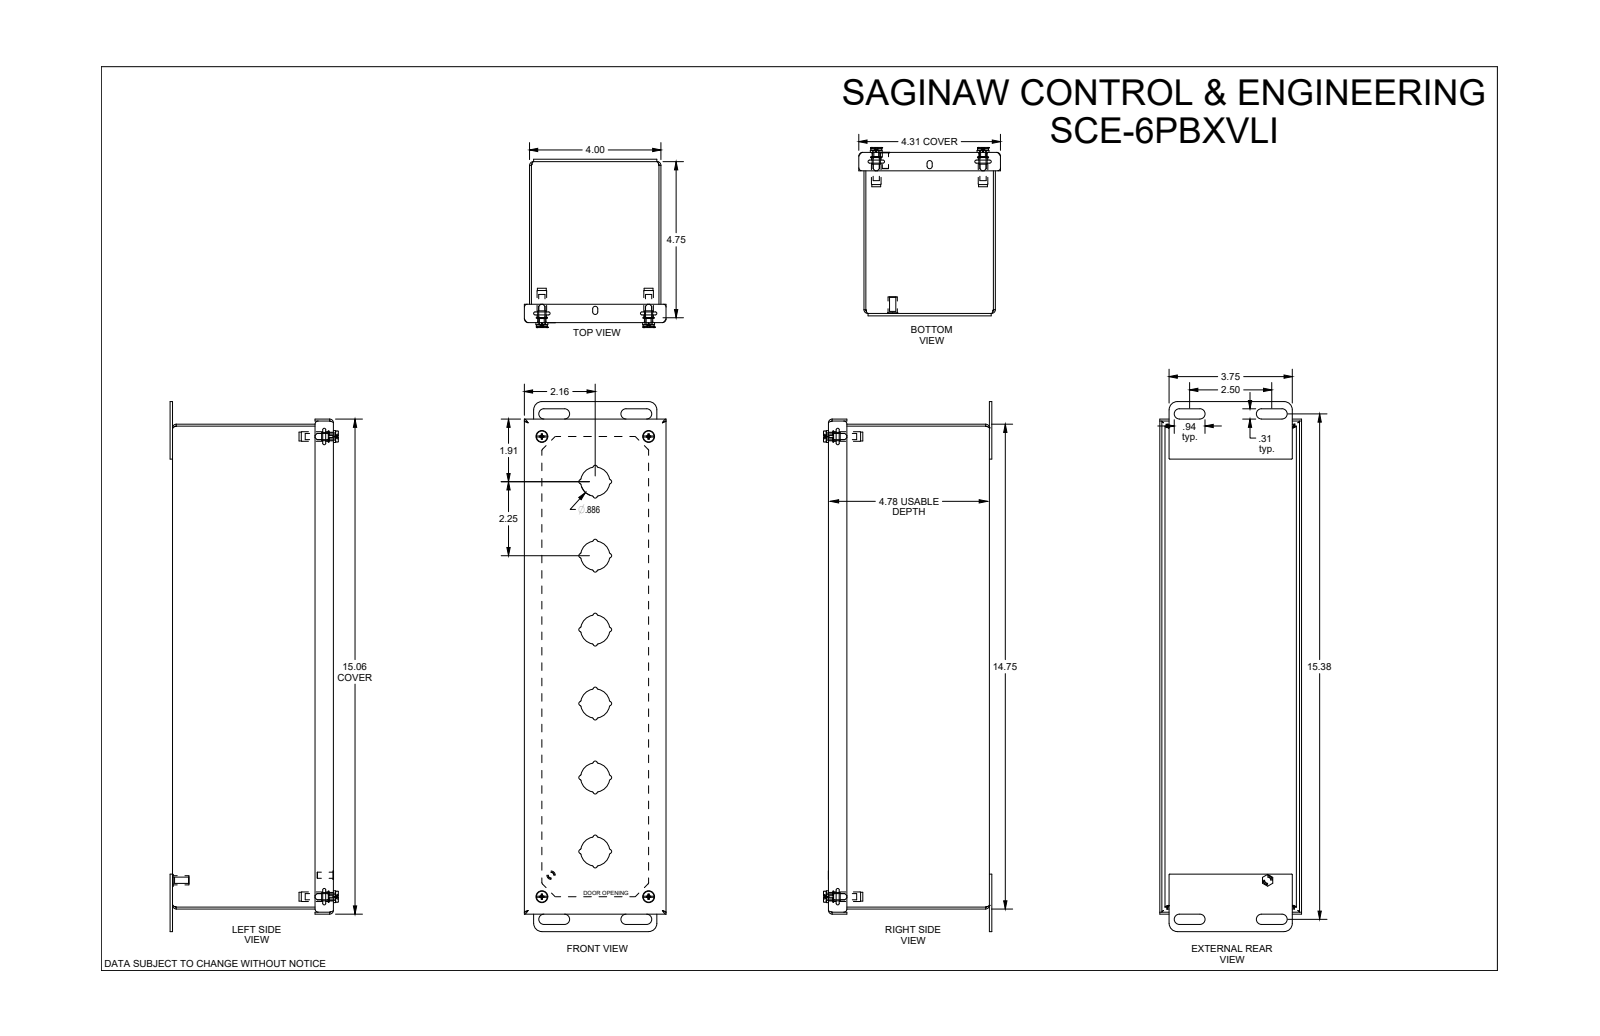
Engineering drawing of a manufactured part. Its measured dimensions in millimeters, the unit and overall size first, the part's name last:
Units: millimetres
Overall size (bounding box): 409.6 × 127.9 × 109.6
Round holes (diameter × count): ⌀4.8 ×5, ⌀5.6 ×4, ⌀6.4 ×4, ⌀6.8 ×4, ⌀8.1 ×4
Round bosses / shafts (diameter × count): ⌀9.2 ×4, ⌀8.6 ×4, ⌀7.4 ×4, ⌀6.9 ×4, ⌀6.6 ×4, ⌀7.1 ×1, ⌀6.5 ×1, ⌀4.8 ×1
Partial cylindrical surfaces — rounded edges, fillets, slot ends (radius × count): R1 ×48, R1.6 ×24, R1.5 ×20, R0.4 ×8, R2.9 ×8, R4 ×8, R6.2 ×8, R11.3 ×6
Main face-to-face distances: 1.5, 100.1, 122.9, 101.6, 98.6, 121.4, 124.4, 373.1, 4, 104
Hole centre spacings: 82.6, 355.6, 357.6, 365, 367, 2, 82.6, 17.8
Volume: 349 700 mm³ · Surface area: 448 500 mm²
Bodies: 3 solids, 524 faces (155 planar, 285 cylindrical, 84 other)
Part name (STEP PRODUCT): SCE-6PBXVLI
STEP written by: SolidWorks 2021 (AUTOMOTIVE_DESIGN)
